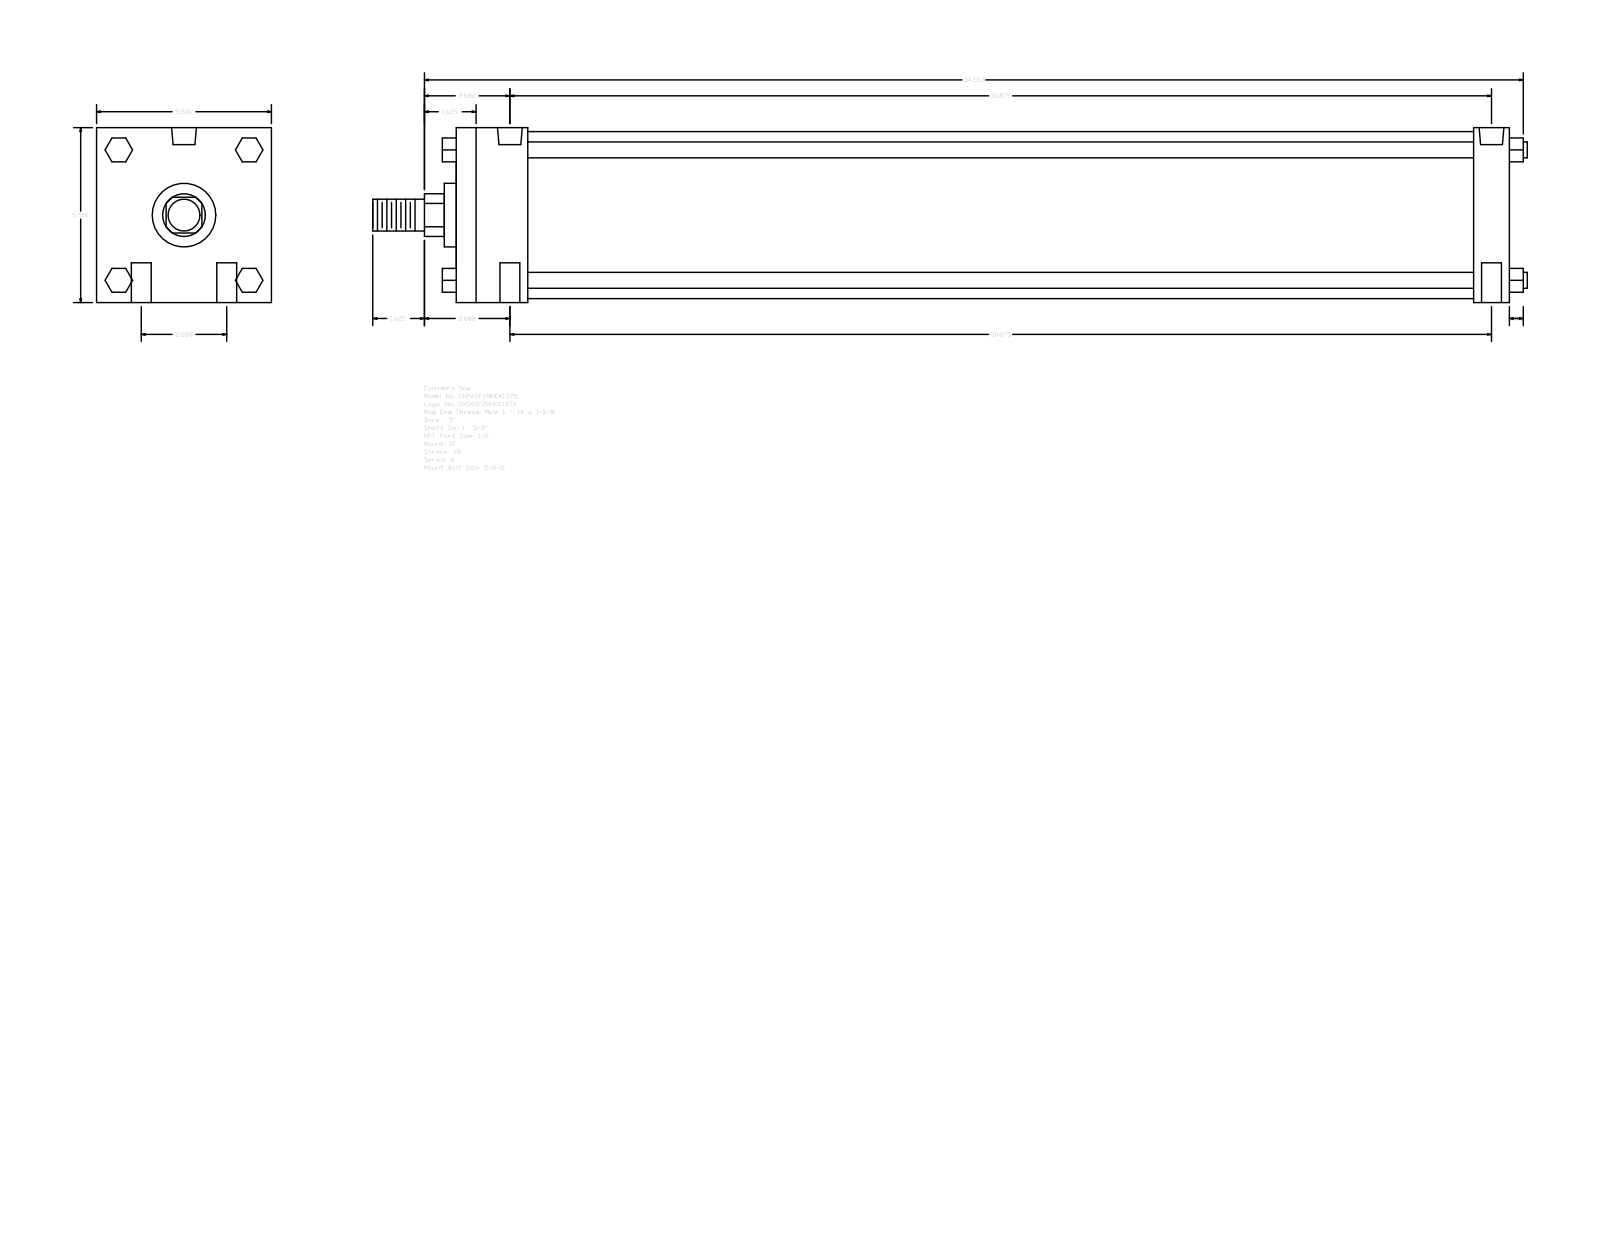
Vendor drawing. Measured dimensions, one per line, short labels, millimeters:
name: A_SF__0500_1.375
written by: GSSL Pune (CONFIG_CONTROL_DESIGN)
unit: mm
bodies: 0 solids, 124 faces (94 planar, 30 cylindrical, 0 other)
size: 922.34 × 139.7 × 139.7
holes: 4× ⌀15.88, 2× ⌀8.73, 2× ⌀19.77
bosses: 4× ⌀12.7, 1× ⌀133.35, 1× ⌀50.8, 1× ⌀34.92, 1× ⌀25.4
rounds: 1× R17.06
face distances: 139.7, 841.37, 57.15, 812.8, 755.65, 784.22, 28.57, 19.05, 52.07, 90.18
hole spacings: 34.13, 784.97, 784.23, 68.26, 787.2, 779.45
